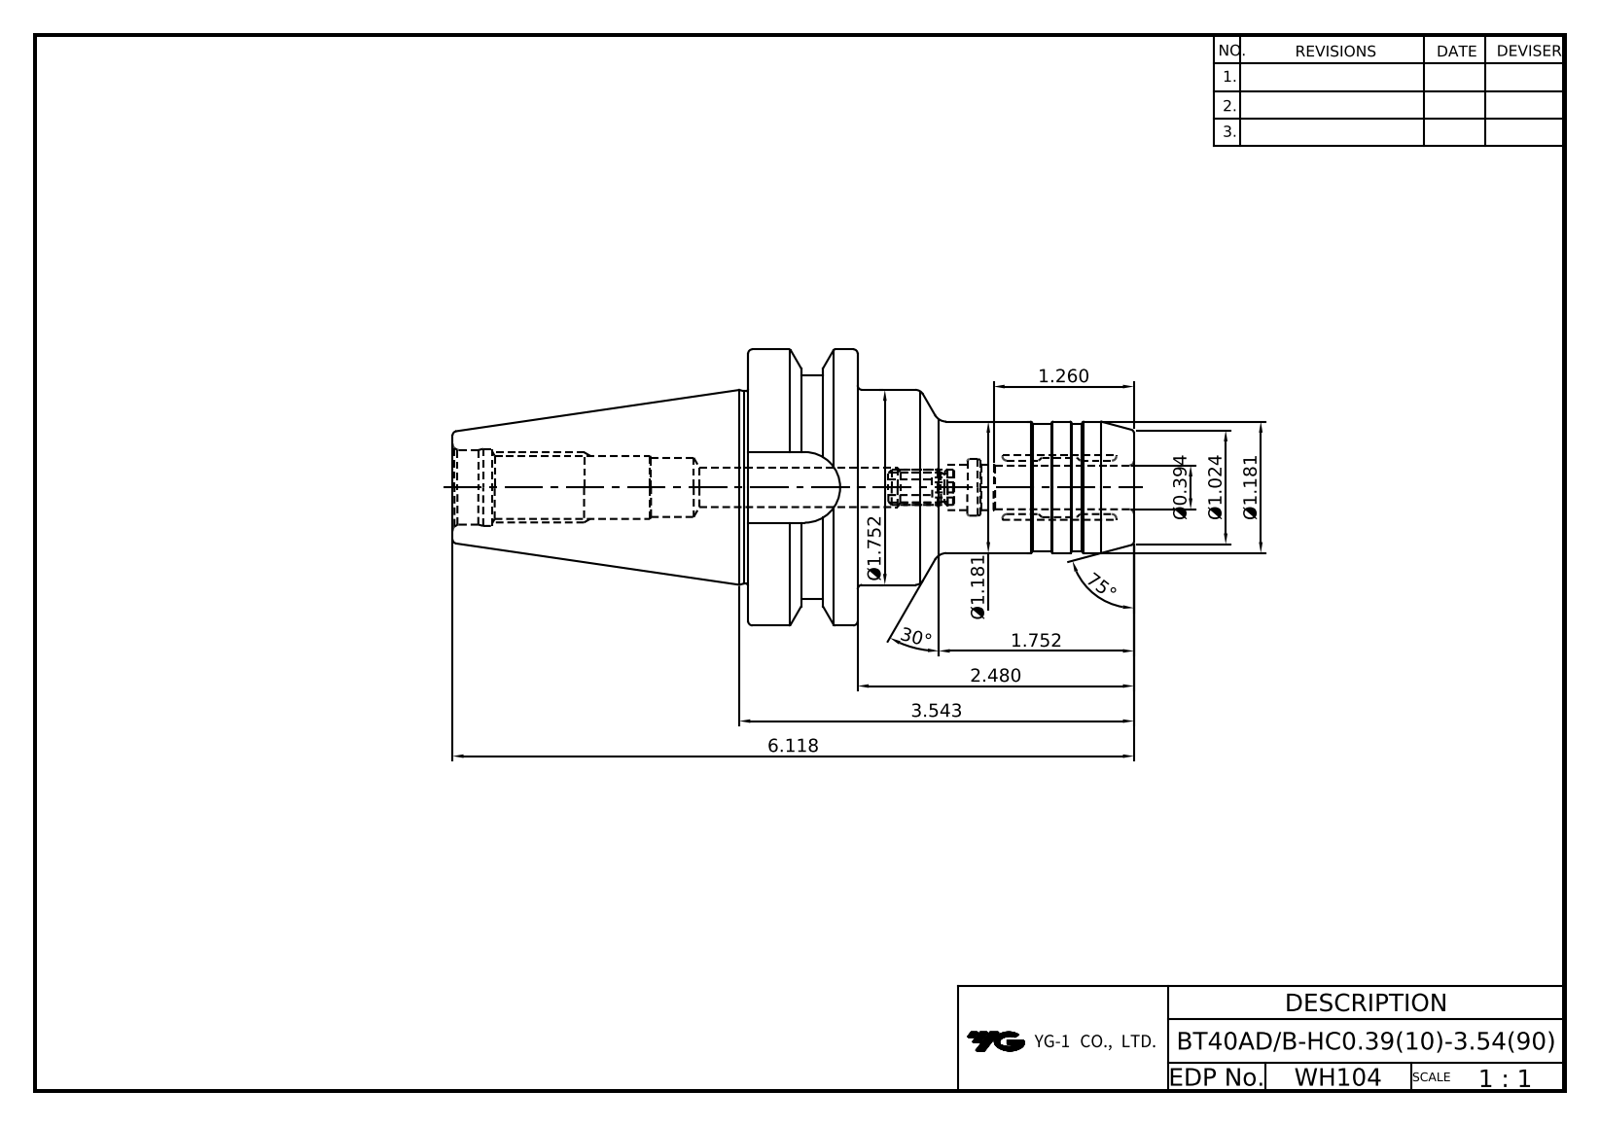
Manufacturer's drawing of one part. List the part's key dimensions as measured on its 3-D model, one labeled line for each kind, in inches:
Part name (STEP PRODUCT): LO-BT40ADB-HC10-90
STEP written by: Autodesk Inventor 2022 (AUTOMOTIVE_DESIGN)
Units: inches
Bodies: 1 solid, 90 faces (21 planar, 34 cylindrical, 35 other)
Overall size (bounding box): 6.118 × 2.48 × 2.48
Volume: 10.65 in³ · Surface area: 47.97 in²
Round holes (diameter × count): ⌀0.128 ×4, ⌀0.157 ×4, ⌀0.272 ×1, ⌀0.354 ×1, ⌀0.394 ×1, ⌀0.417 ×1, ⌀0.531 ×1, ⌀0.545 ×1, ⌀0.669 ×1, ⌀0.693 ×1
Round bosses / shafts (diameter × count): ⌀2.48 ×1, ⌀2.008 ×1, ⌀1.752 ×1, ⌀1.732 ×1, ⌀1.181 ×1, ⌀1.142 ×1
Partial cylindrical surfaces — rounded edges, fillets, slot ends (radius × count): R0.317 ×1
Main face-to-face distances: 0.984, 3.465, 2.48, 1.78, 0.673, 0.311, 2.791, 0.476, 0.197, 0.508
